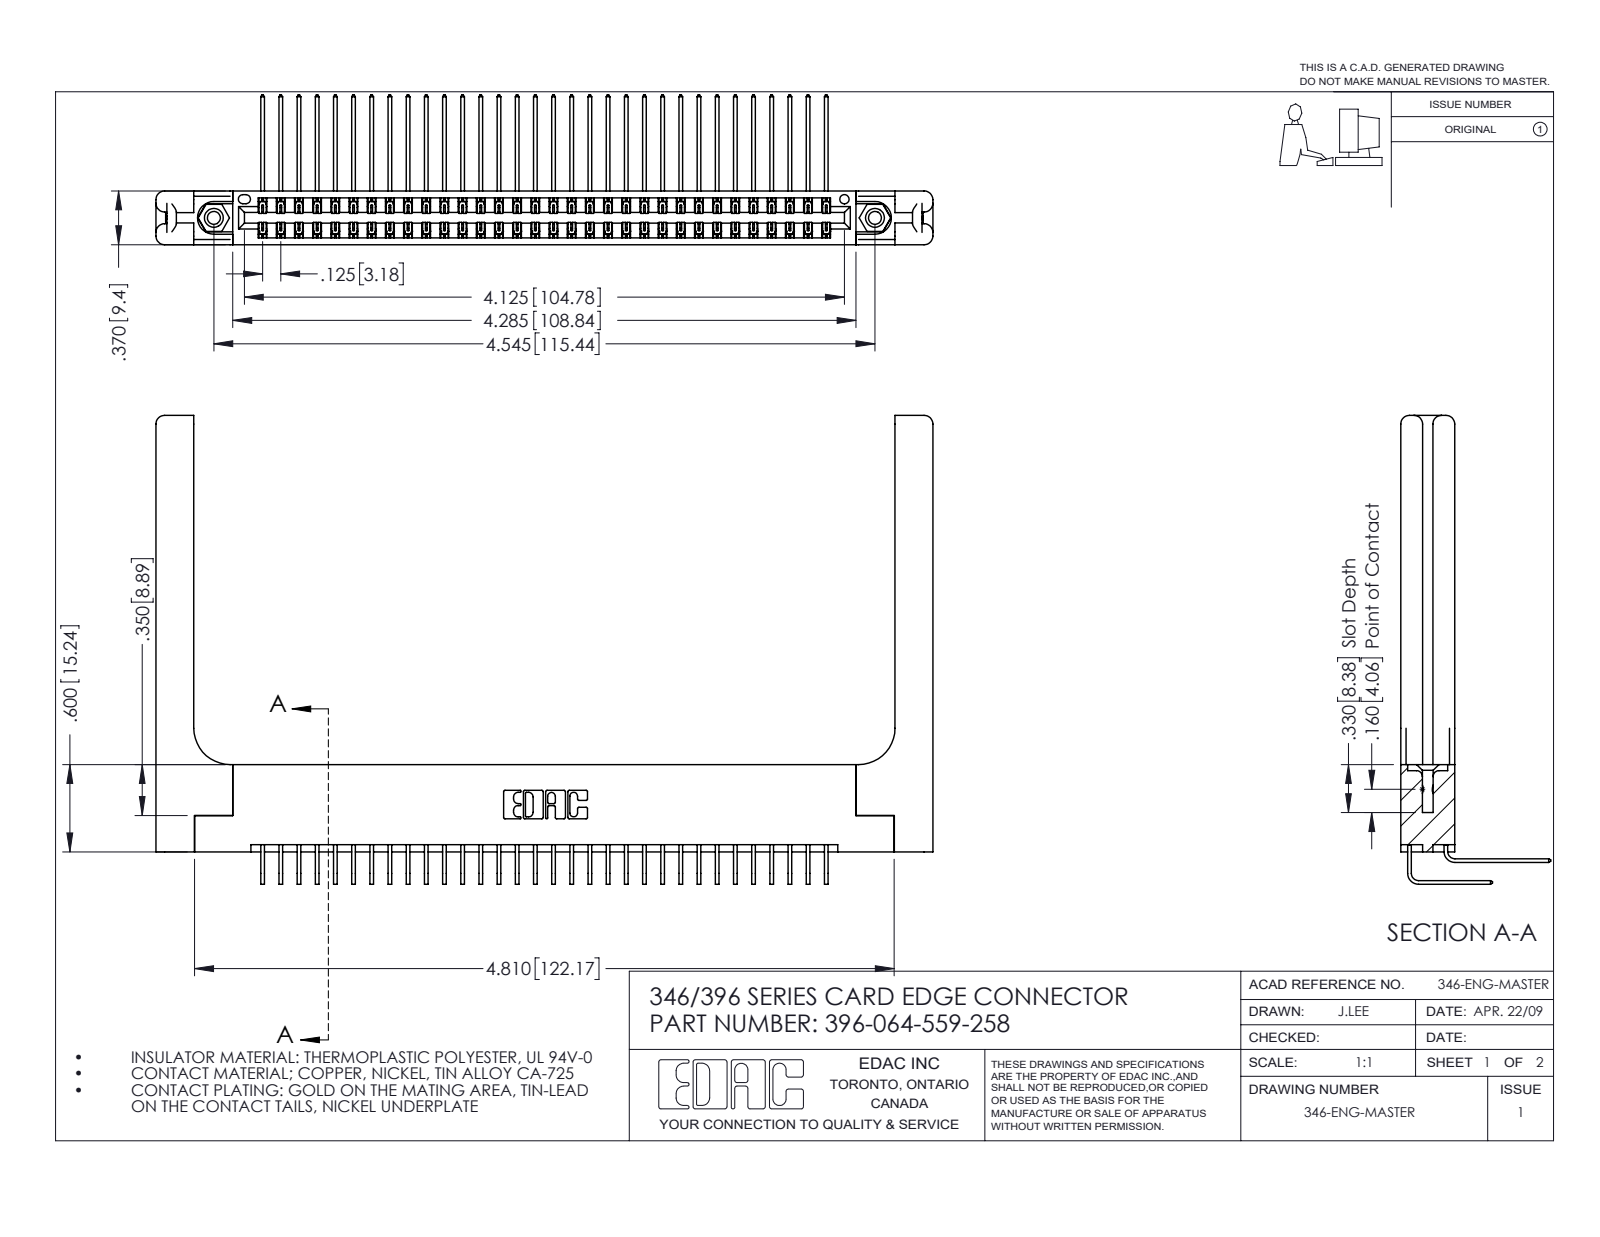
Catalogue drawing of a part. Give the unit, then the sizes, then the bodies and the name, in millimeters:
Units: millimetres
Overall size (bounding box): 135.7 × 81.9 × 26.2
Round holes (diameter × count): ⌀2.3 ×2, ⌀3.2 ×2, ⌀4 ×2, ⌀1.6 ×1
Round bosses / shafts (diameter × count): ⌀3.9 ×2
Partial cylindrical surfaces — rounded edges, fillets, slot ends (radius × count): R0.2 ×96, R0.3 ×22, R1.5 ×16, R0.2 ×6, R0.8 ×6, R0.7 ×3, R0.4 ×2, R0.6 ×2
Main face-to-face distances: 1.2, 9.4, 8.2, 1.8, 0.6, 3.8, 3.8, 6.4, 7.6, 7
Hole centre spacings: 6.2, 110.2, 115.4
Volume: 21 010 mm³ · Surface area: 25 170 mm²
Bodies: 69 solids, 3834 faces (2592 planar, 1182 cylindrical, 60 other)
Part name (STEP PRODUCT): 345-250-001_345-250-001-102; 346-220-058_345-220-058; 346 Part_Flush Mounting Lugs - 0.156 Dia-TH; 345-292-001_559 Tail - 2 (+2 more)
STEP written by: SolidWorks 2016 (CONFIG_CONTROL_DESIGN)
